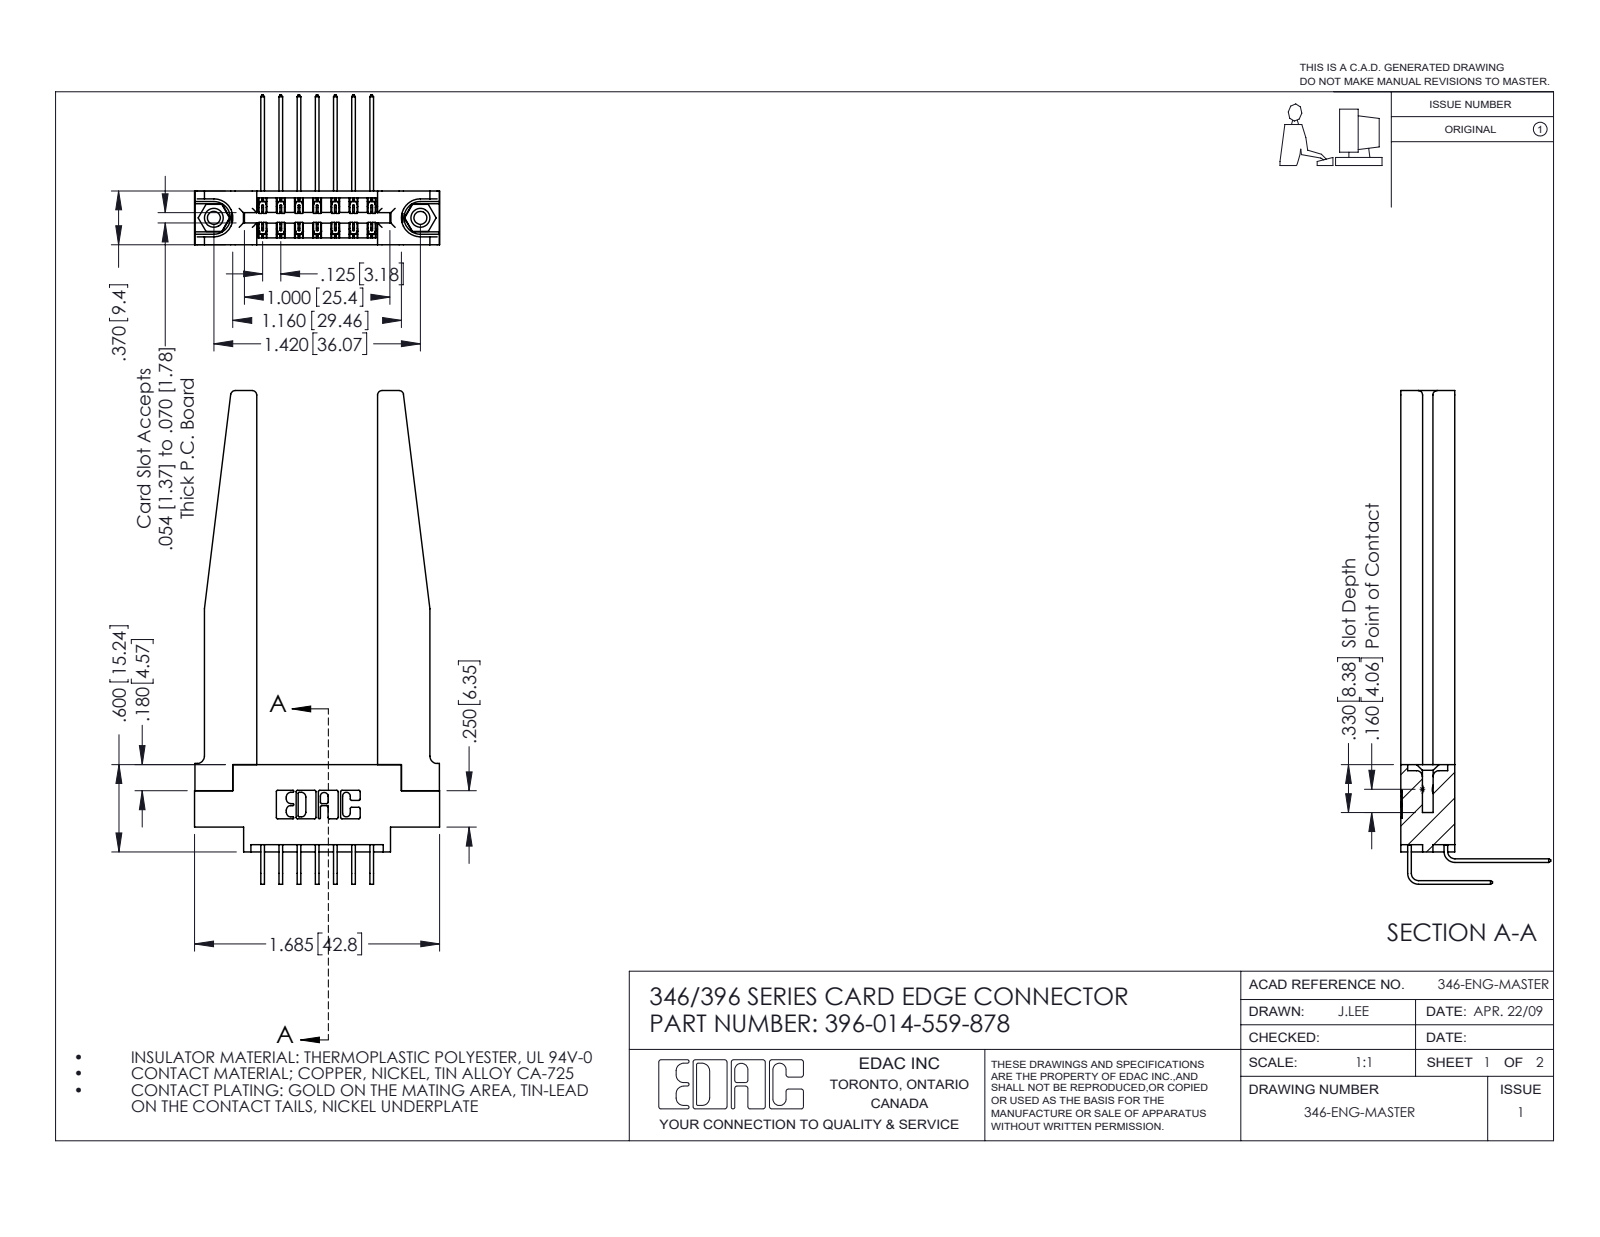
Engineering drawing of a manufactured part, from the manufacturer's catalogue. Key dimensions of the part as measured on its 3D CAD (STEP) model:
Part name (STEP PRODUCT): 345-292-001_558 559 Tail - 1; 345-292-001_559 Tail - 2; 346-220-078_345-220-078; 345-250-001_345-250-001-102 (+2 more)
STEP written by: SolidWorks 2016 (CONFIG_CONTROL_DESIGN)
Units: inches
Bodies: 19 solids, 1116 faces (740 planar, 324 cylindrical, 52 other)
Overall size (bounding box): 3.393 × 1.685 × 1.03
Volume: 0.655 in³ · Surface area: 18.31 in²
Round holes (diameter × count): ⌀0.089 ×2, ⌀0.125 ×2, ⌀0.156 ×2, ⌀0.064 ×1
Round bosses / shafts (diameter × count): ⌀0.155 ×2
Partial cylindrical surfaces — rounded edges, fillets, slot ends (radius × count): R0.01 ×22, R0.006 ×21, R0.03 ×8, R0.007 ×6, R0.031 ×6, R0.05 ×4, R0.026 ×3, R0.014 ×2
Main face-to-face distances: 0.37, 0.15, 0.22, 0.072, 0.048, 0.25, 0.148, 0.831, 0.322, 0.102
Hole centre spacings: 0.246, 1.217, 1.42
